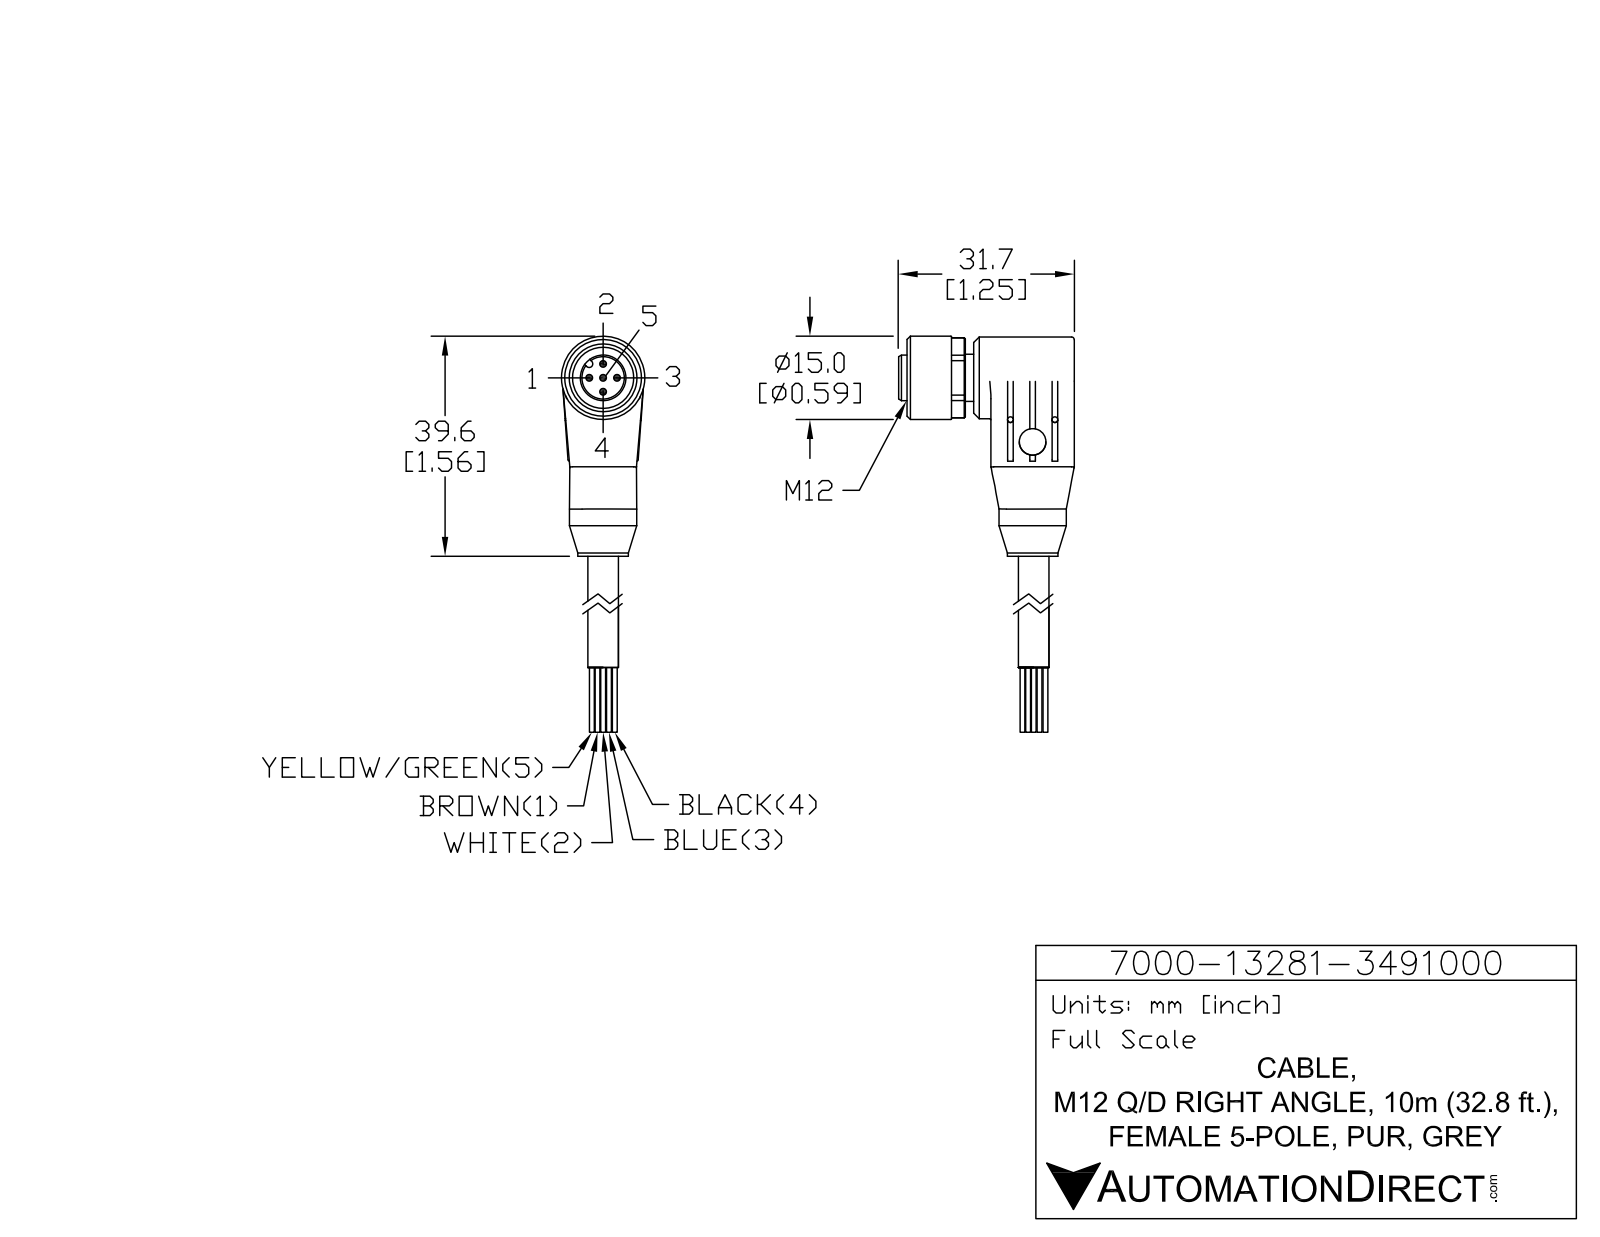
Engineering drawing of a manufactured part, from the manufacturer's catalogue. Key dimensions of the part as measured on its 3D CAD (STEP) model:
Part name (STEP PRODUCT): 7000-13281-3491000
STEP written by: SolidWorks 2015 (AUTOMOTIVE_DESIGN)
Units: millimetres
Bodies: 1 solid, 165 faces (70 planar, 61 cylindrical, 34 other)
Overall size (bounding box): 59.6 × 31.6 × 15
Volume: 9 143 mm³ · Surface area: 4 032 mm²
Round holes (diameter × count): ⌀1.2 ×5, ⌀1.05 ×4, ⌀4.8 ×1, ⌀11 ×1
Round bosses / shafts (diameter × count): ⌀15 ×1, ⌀14.7 ×1, ⌀12.1 ×1, ⌀9.1 ×1, ⌀8.5 ×1, ⌀8.2 ×1, ⌀6.5 ×1
Partial cylindrical surfaces — rounded edges, fillets, slot ends (radius × count): R0.5 ×4, R0.3 ×2, R0.65 ×1, R7.2 ×1
Main face-to-face distances: 15, 1.5, 19.6, 4.6, 12, 18.1, 3.1, 3, 7.6, 16.6
Hole centre spacings: 2.5, 3.54, 5, 8
